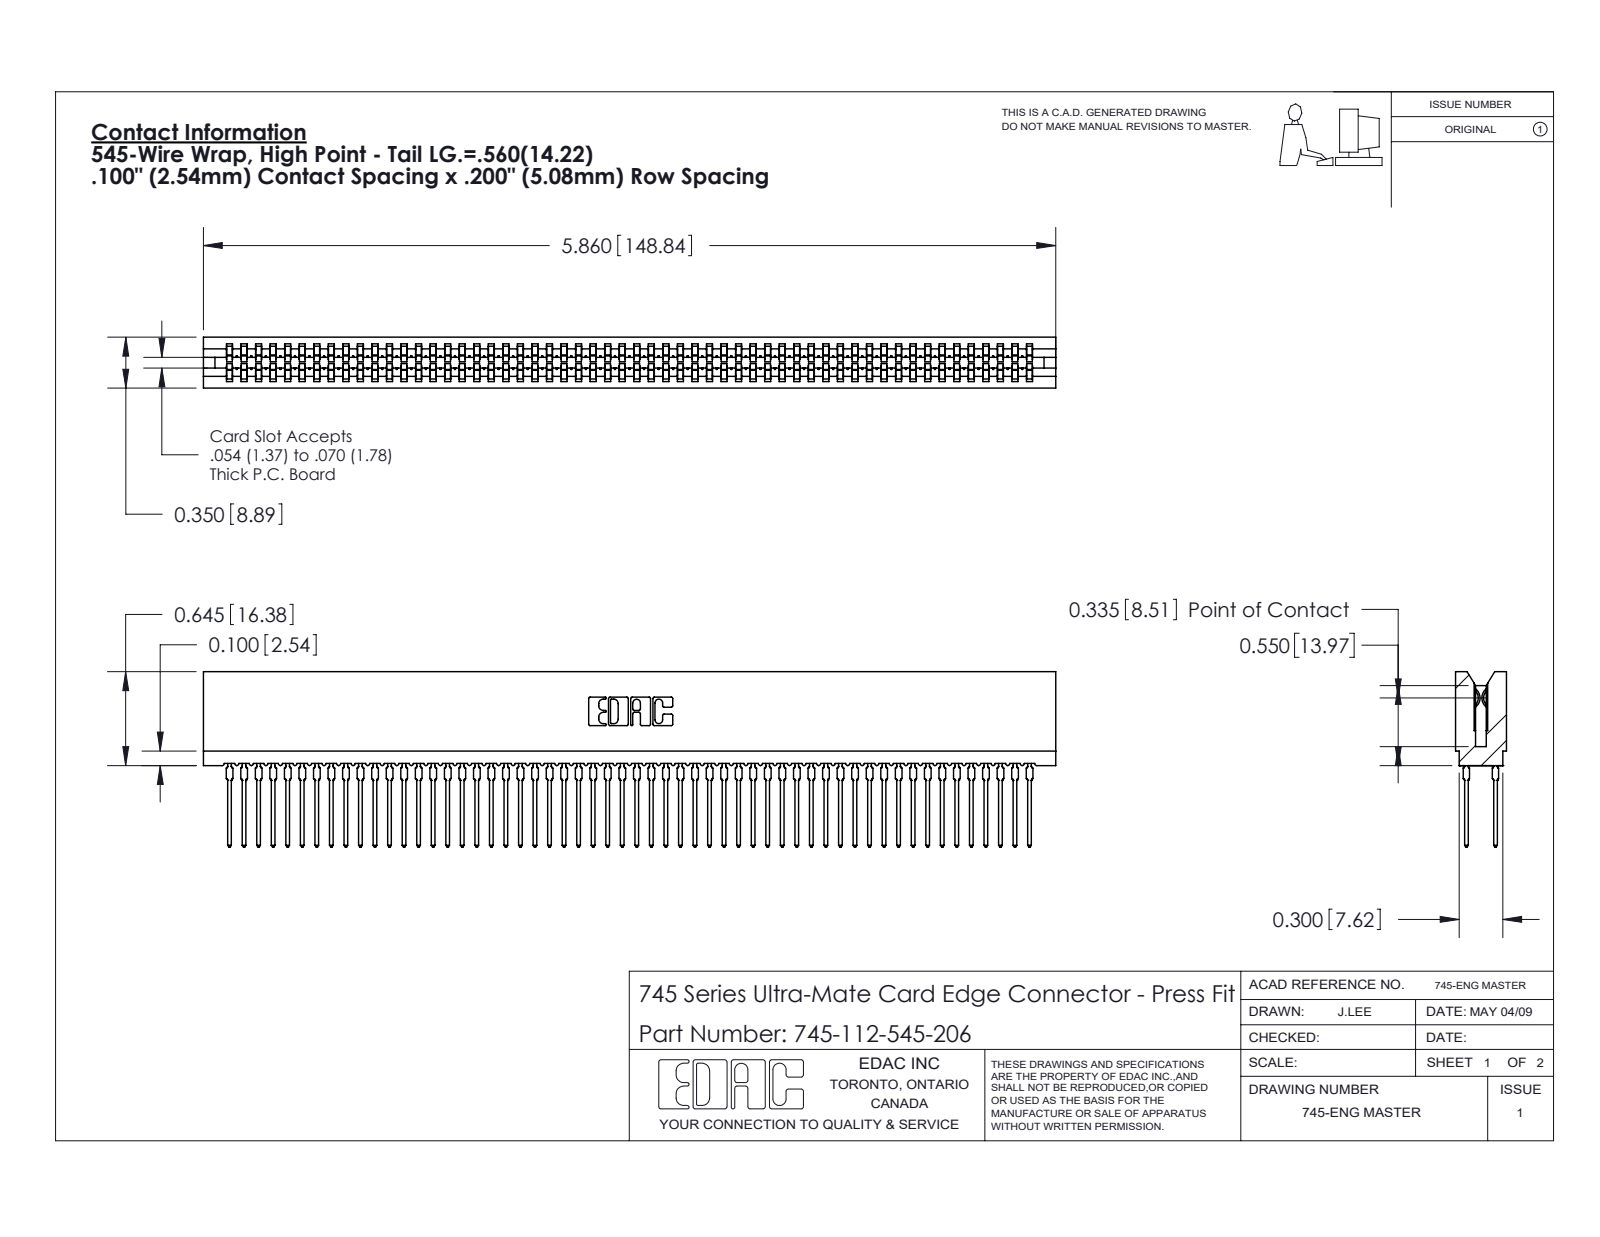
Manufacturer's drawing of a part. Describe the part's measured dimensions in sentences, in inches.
The part is named "745-292-001_545; 745 Part_Insulator Option - 06; 745-112-545-206". Its 3-D file was written by "SolidWorks 2020 (CONFIG_CONTROL_DESIGN)". It is 113 solids with 10120 faces: 5208 planar, 2000 cylindrical and 2912 other. Overall it measures 5.86 by 1.206 by 0.35 inches. Its volume is 0.835 cubic inches and its surface area 46.33 square inches. Partial cylindrical surfaces (rounded edges, fillets, slot ends): 224 of radius 0.021, 112 of radius 0.015, 22 of radius 0.01, 8 of radius 0.005, 8 of radius 0.011, 6 of radius 0.007, 6 of radius 0.031, 3 of radius 0.026. The main face-to-face distances are 0.063, 0.287, 0.35, 0.2, 0.045, 0.305, 0.018, 0.243, 0.138, 0.212.
